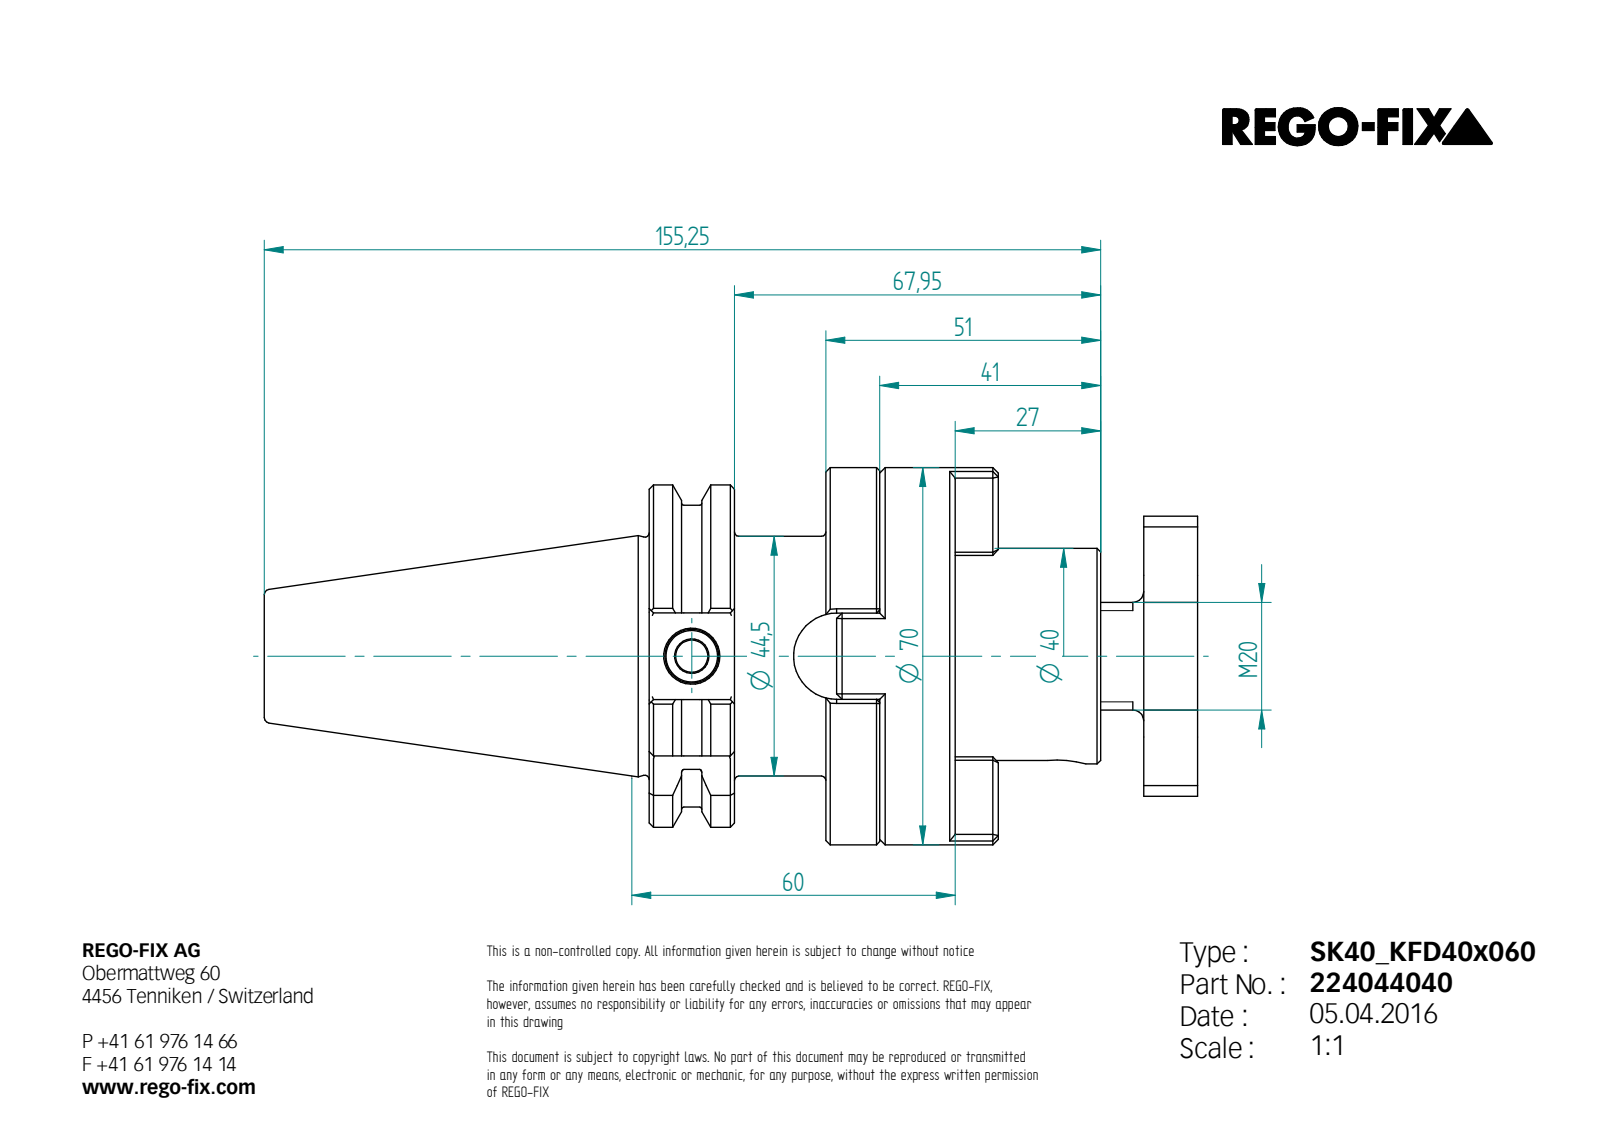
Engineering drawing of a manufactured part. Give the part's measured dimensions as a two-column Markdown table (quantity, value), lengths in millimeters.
| quantity | value |
| --- | --- |
| STEP written by | Unknown (AUTOMOTIVE_DESIGN) |
| units | millimeters |
| bodies | 3 solids, 250 faces (132 planar, 50 cylindrical, 68 other) |
| overall size | 173.25 × 70 × 70 |
| volume | 263 837 mm³ |
| surface area | 56 106 mm² |
| round holes (diameter × count) | 6 × 1, 10 × 1, 13.84 × 1, 17 × 1, 17.29 × 1, 21 × 1, 40 × 1 |
| round bosses / shafts (diameter × count) | 70 × 1, 44.5 × 1, 39.4 × 1, 20 × 1 |
| partial cylindrical surfaces (radius × count) | 0.5 × 13, 5 × 6, 8 × 1, 26 × 1, 28 × 1, 31.77 × 1 |
| main face-to-face distances | 10, 59, 14, 24, 69, 45, 49, 8, 18, 27 |
